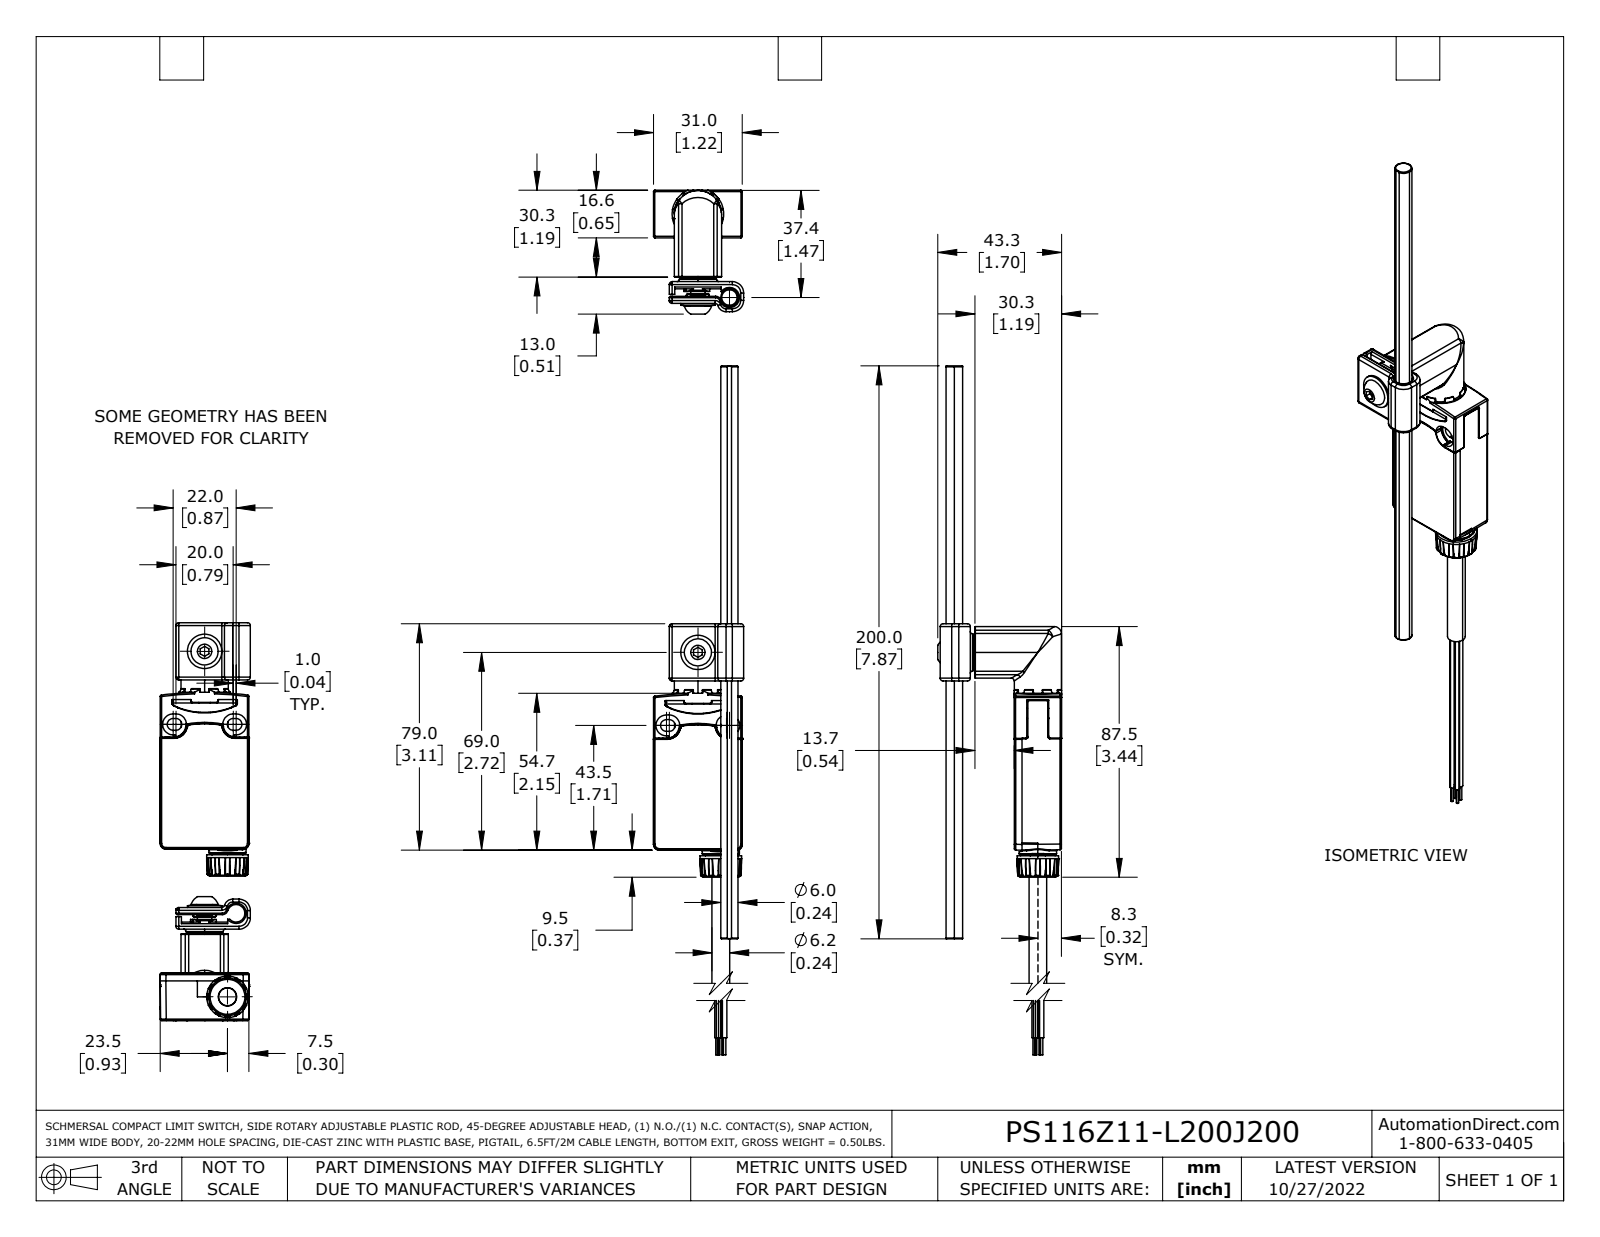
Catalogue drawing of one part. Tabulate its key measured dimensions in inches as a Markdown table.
| quantity | value |
| --- | --- |
| part name | PS116Z11-L200J200_Default |
| STEP written by | SolidWorks 2021 (CONFIG_CONTROL_DESIGN) |
| units | inches |
| bodies | 2 solids, 1185 faces (361 planar, 488 cylindrical, 336 other) |
| overall size | 11.28 × 1.703 × 1.24 |
| volume | 2.831 in³ |
| surface area | 35.13 in² |
| round holes (diameter × count) | 0.48 × 2, 0.079 × 1, 0.24 × 1, 0.252 × 1, 0.571 × 1, 0.583 × 1 |
| round bosses / shafts (diameter × count) | 0.059 × 4, 0.031 × 4, 0.512 × 2, 0.65 × 1, 0.571 × 1, 0.567 × 1, 0.524 × 1, 0.475 × 1 |
| partial cylindrical surfaces (radius × count) | 0.008 × 143, 0.004 × 61, 0.02 × 37, 0.039 × 27, 0.079 × 12, 0.014 × 10, 0.012 × 6, 0.118 × 5 |
| main face-to-face distances | 0.65, 0.652, 0.098, 0.201, 0.228, 0.709, 1.587, 0.937, 1.358, 1.22 |
| hole center spacings | 0.315, 1.154, 1.227 |
